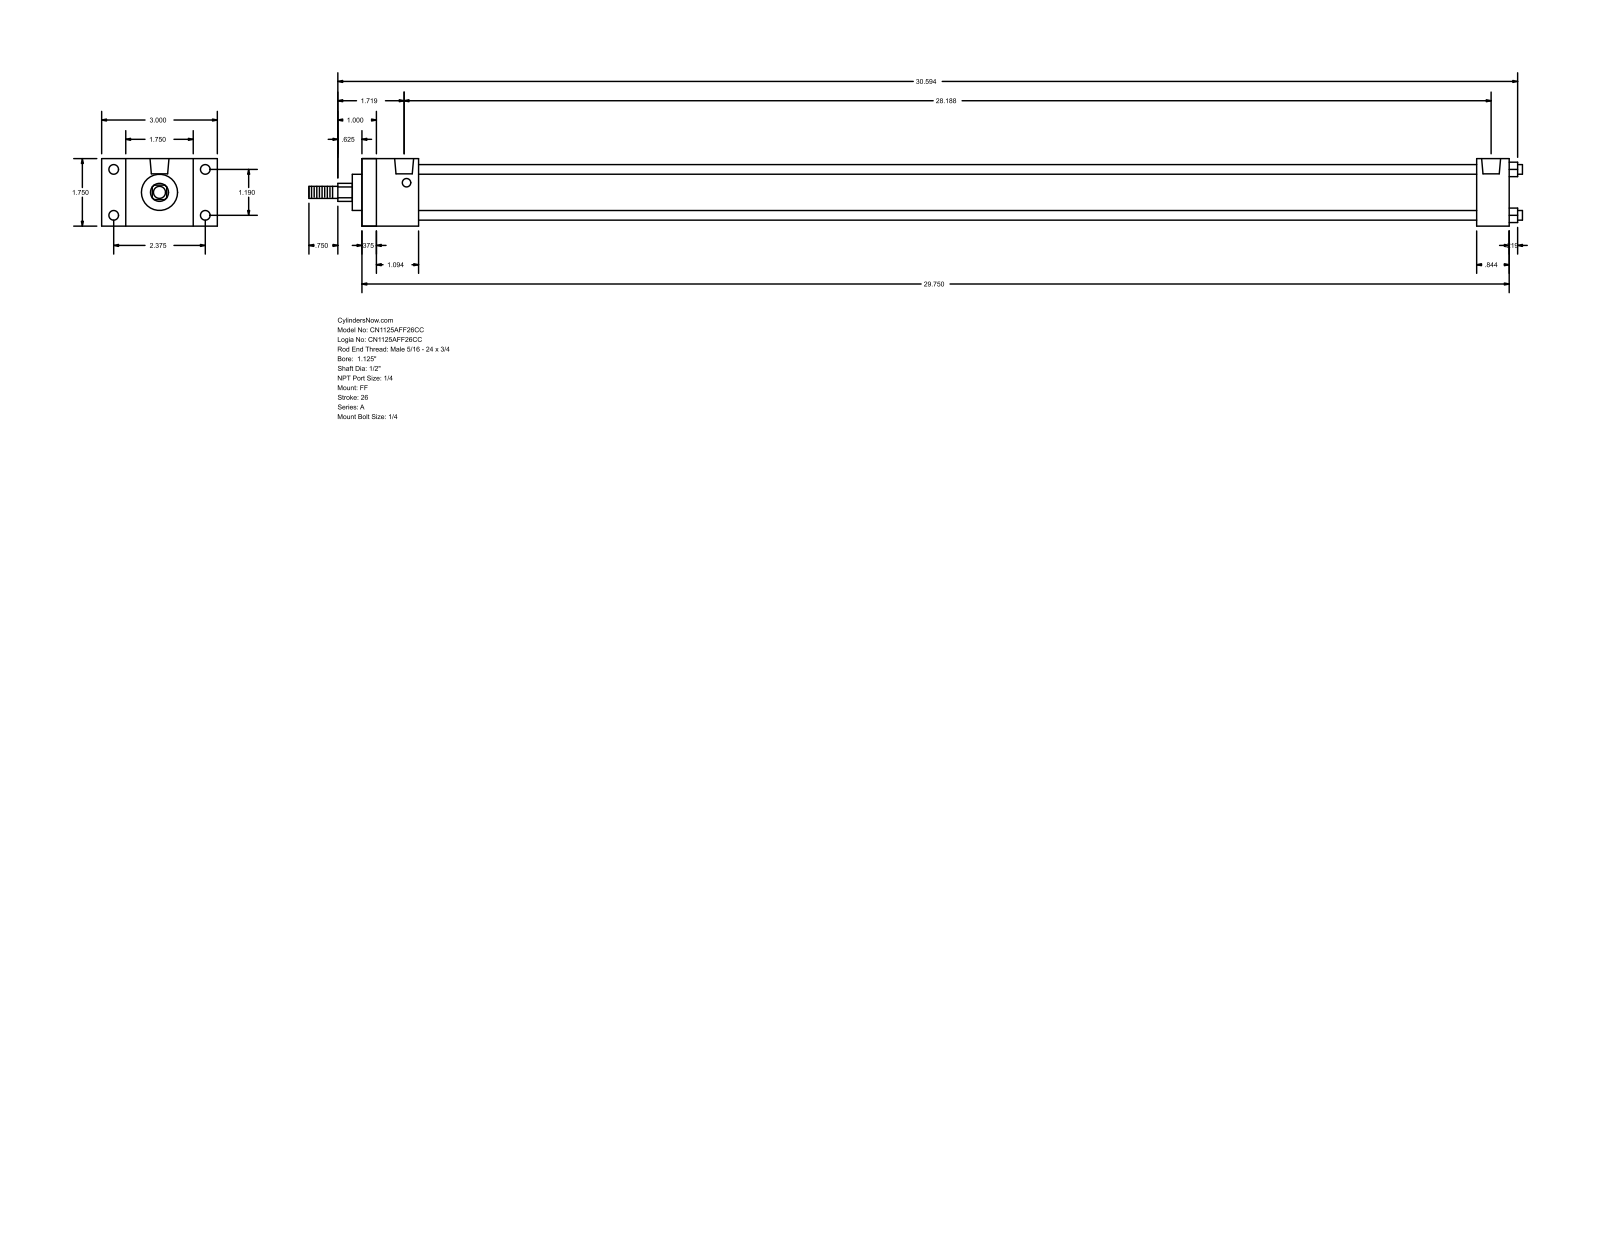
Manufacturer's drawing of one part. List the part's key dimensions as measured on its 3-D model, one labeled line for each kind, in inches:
Part name (STEP PRODUCT): A_FF__0112_0.5
STEP written by: GSSL Pune (CONFIG_CONTROL_DESIGN)
Units: inches
Bodies: 0 solids, 92 faces (64 planar, 28 cylindrical, 0 other)
Overall size (bounding box): 31.469 × 3 × 1.75
Round holes (diameter × count): ⌀0.219 ×4, ⌀0.25 ×4, ⌀0.492 ×2
Round bosses / shafts (diameter × count): ⌀0.25 ×4, ⌀1.255 ×1, ⌀0.937 ×1, ⌀0.5 ×1, ⌀0.313 ×1
Partial cylindrical surfaces — rounded edges, fillets, slot ends (radius × count): R0.234 ×1
Main face-to-face distances: 1.75, 29.75, 0.375, 29.375, 0.625, 28.906, 28.531, 0.844, 1.469, 1.094
Hole centre spacings: 1.19, 2.375, 2.656, 28.063, 0.062, 0.063, 28.125, 28.125
